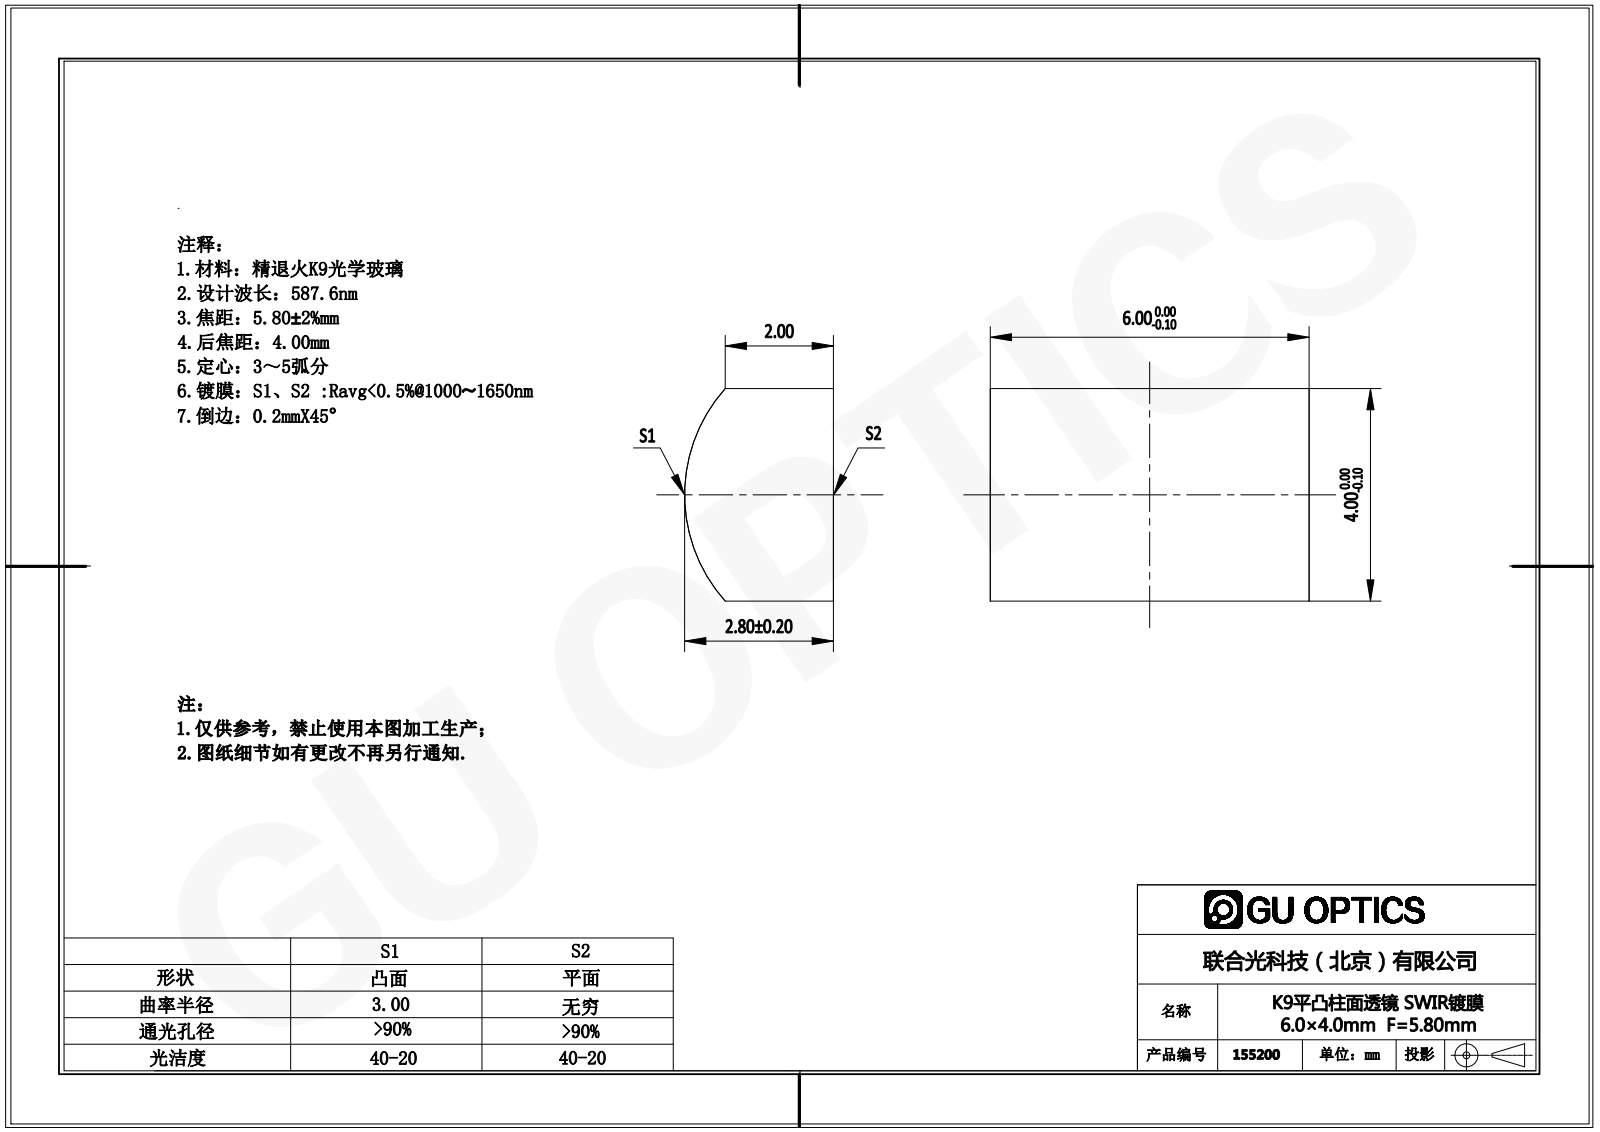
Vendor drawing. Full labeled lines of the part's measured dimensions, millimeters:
Part name (STEP PRODUCT): 155002
STEP written by: SolidWorks 2016 (AUTOMOTIVE_DESIGN)
Units: millimetres
Bodies: 1 solid, 6 faces (5 planar, 1 cylindrical, 0 other)
Overall size (bounding box): 6 × 4 × 2.8
Volume: 61 mm³ · Surface area: 95 mm²
Partial cylindrical surfaces — rounded edges, fillets, slot ends (radius × count): R3 ×1
Main face-to-face distances: 4, 6
